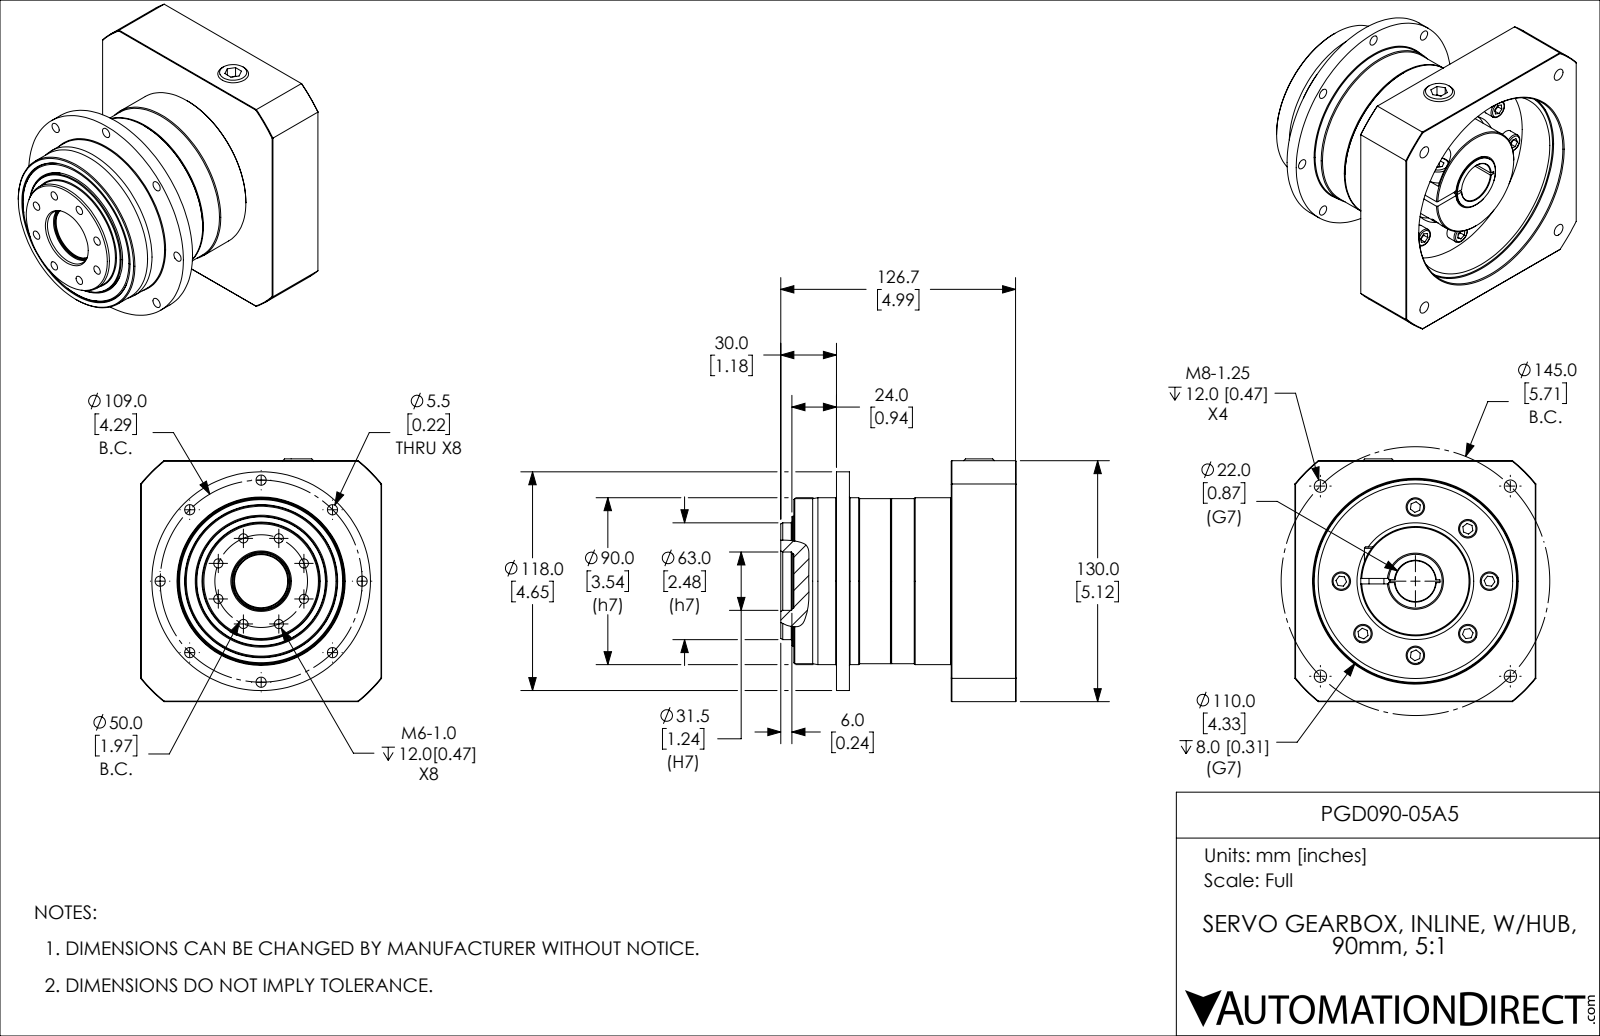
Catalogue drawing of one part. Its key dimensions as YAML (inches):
part_name: "PGD090-05A5"
step_written_by: "SolidWorks 2015 (AUTOMOTIVE_DESIGN)"
units: inches
bodies: {solids: 4, faces: 406, planar: 190, cylindrical: 146, other: 70}
overall_size: [5.134, 5.094, 5]
volume: 53.74
surface_area: 195.6
round_holes:
  - {diameter: 0.217, count: 8}
  - {diameter: 0.194, count: 7}
  - {diameter: 0.315, count: 3}
  - {diameter: 0.262, count: 2}
  - {diameter: 0.262, count: 2}
  - {diameter: 0.194, count: 1}
  - {diameter: 0.197, count: 1}
  - {diameter: 0.512, count: 1}
  - {diameter: 0.567, count: 1}
  - {diameter: 0.709, count: 1}
  - {diameter: 0.787, count: 1}
  - {diameter: 1.102, count: 1}
round_bosses_or_shafts:
  - {diameter: 0.394, count: 7}
  - {diameter: 4.646, count: 1}
  - {diameter: 3.543, count: 1}
  - {diameter: 3.504, count: 1}
  - {diameter: 2.48, count: 1}
  - {diameter: 2.126, count: 1}
  - {diameter: 1.654, count: 1}
  - {diameter: 0.654, count: 1}
partial_cylinders:
  - {radius: 0.016, count: 6}
  - {radius: 0.276, count: 1}
  - {radius: 3.276, count: 1}
face_to_face_distances: [3.35, 5.094, 0.157, 1.378, 4.728, 3.819, 3.587, 0.236, 0.909, 1.142]
hole_center_spacings: [1.293, 2.681, 3.078, 0.984, 1.392, 1.819, 1.981, 1.989]
